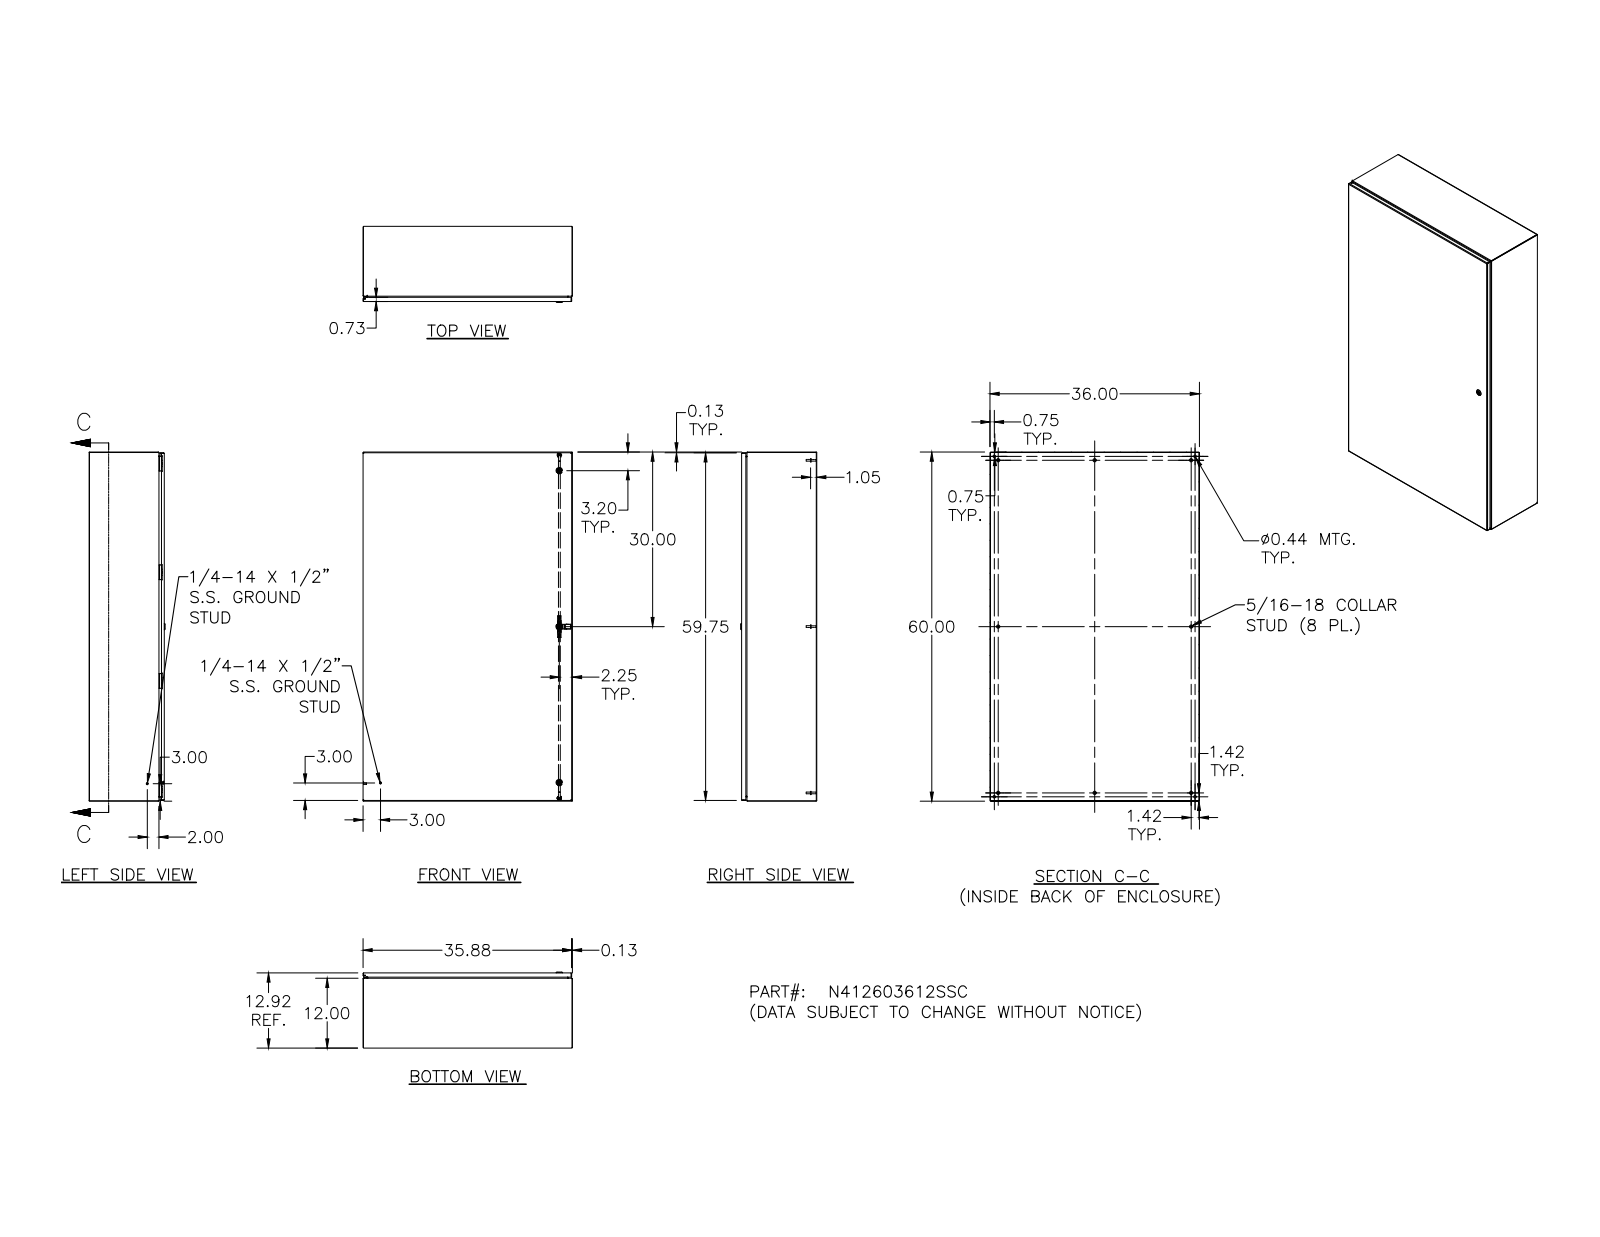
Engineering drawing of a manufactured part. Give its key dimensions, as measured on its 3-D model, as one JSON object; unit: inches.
{"part_name": "N412603612SSC; N412603612SSCBTB; N4126012SSCLS; N4126012SSCRS (+8 more)", "step_written_by": "Autodesk Inventor 2011 (AUTOMOTIVE_DESIGN)", "units": "inches", "bodies": {"solids": 81, "faces": 2655, "planar": 982, "cylindrical": 992, "other": 681}, "overall_size": [60.127, 36, 13.075], "volume_in3": 524.2, "surface_area_in2": 14148, "round_holes": [[0.093, 8], [0.152, 8], [0.167, 8], [0.172, 8], [0.187, 8], [0.197, 5], [0.156, 4], [0.165, 4], [0.437, 4], [0.106, 2], [0.16, 2], [0.169, 2]], "round_bosses_or_shafts": [[0.25, 18], [0.563, 8], [0.36, 8], [0.32, 8], [0.3, 8], [0.275, 8], [0.256, 8], [0.164, 8]], "partial_cylinders_radius": [[0.05, 50], [0.031, 36], [0.016, 34], [0.125, 32], [0.012, 30], [0.02, 20], [0.105, 18], [0.032, 16]], "face_to_face_distances": [0.074, 12.843, 12.769, 12.917, 35.926, 59.926, 35.852, 36, 59.852, 60], "hole_center_spacings": [18.667, 37.333, 18.667, 56, 0.5, 0.656, 1.307, 18.673]}
